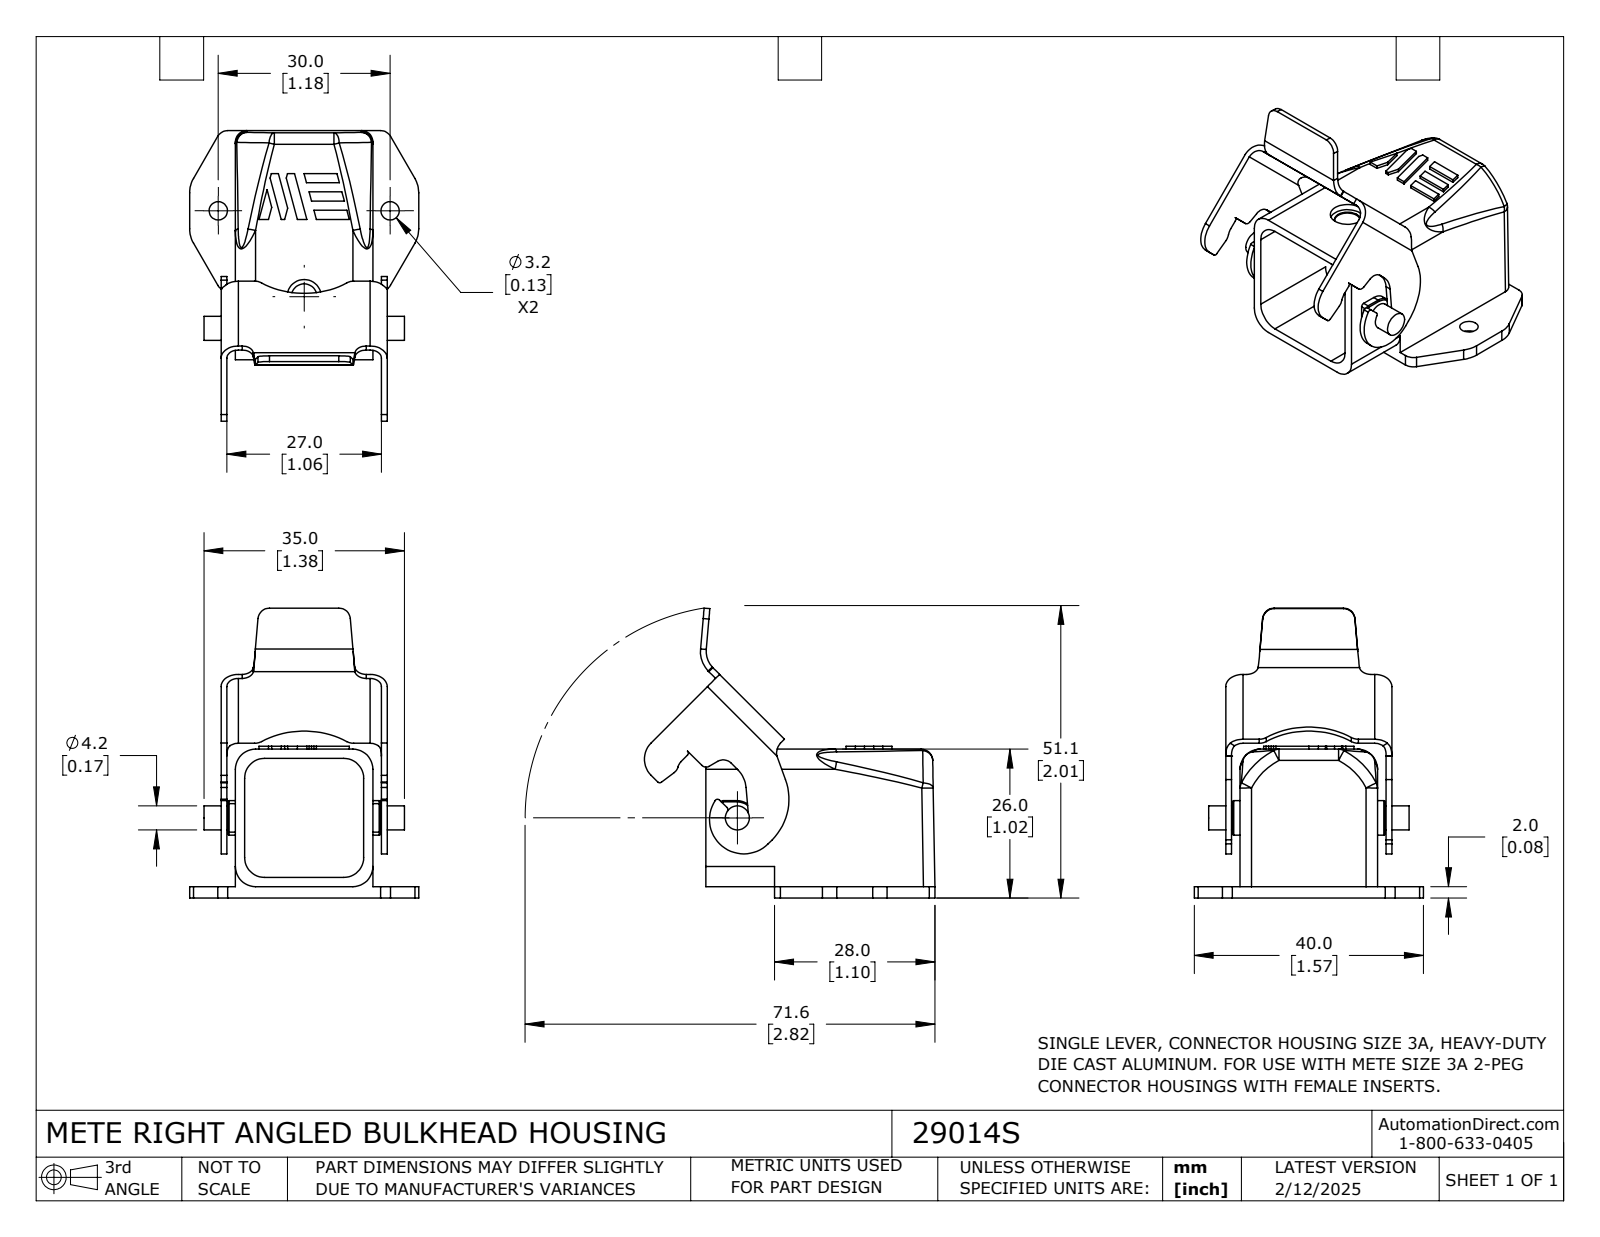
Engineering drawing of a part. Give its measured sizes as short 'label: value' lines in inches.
name: 29014S
written by: SolidWorks 2024 (CONFIG_CONTROL_DESIGN)
unit: in
bodies: 1 solid, 218 faces (103 planar, 87 cylindrical, 28 other)
size: 1.997 × 1.993 × 1.575
volume: 0.553 in³; area: 17.09 in²
holes: 2× ⌀0.126, 1× ⌀0.177, 1× ⌀0.236
bosses: 1× ⌀0.165
rounds: 16× R0.079, 8× R0.138, 6× R0.008, 6× R0.02, 6× R0.197, 3× R0.118, 2× R0.157, 1× R0.039
face distances: 0.063, 0.882, 0.945, 0.039, 0.819, 1.043, 1.102, 0.098, 0.98, 0.059
hole spacings: 0.835, 1.181
